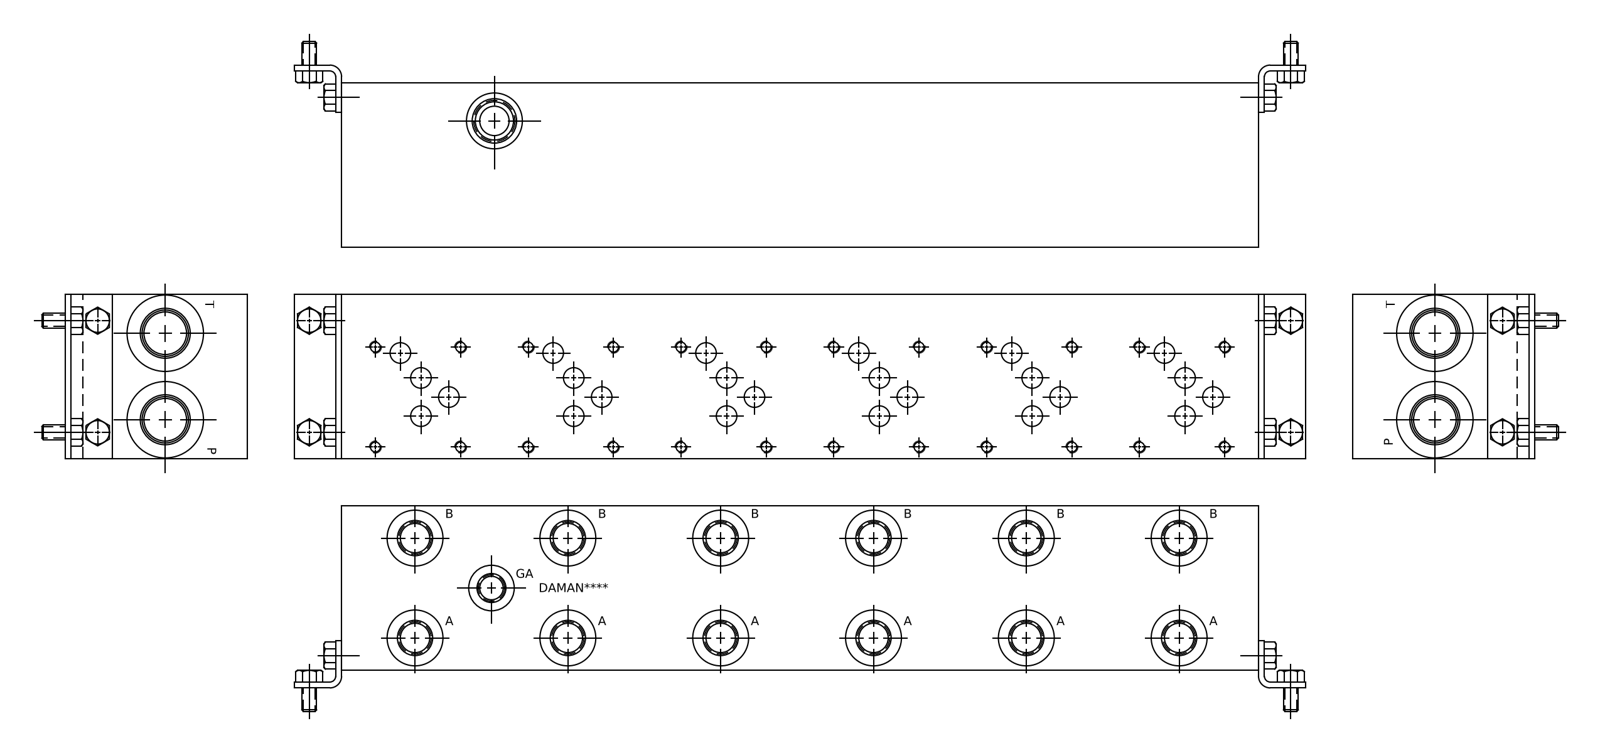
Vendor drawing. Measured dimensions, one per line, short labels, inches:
name: Part_AD05P063S_C_3D
written by: Autodesk Inventor 2020 (AUTOMOTIVE_DESIGN)
unit: in
bodies: 1 solid, 1038 faces (497 planar, 171 cylindrical, 370 other)
size: 19.5 × 3.5 × 3.5
volume: 226.7 in³; area: 367 in²
holes: 24× ⌀0.201, 24× ⌀0.25, 24× ⌀0.438, 12× ⌀0.625, 12× ⌀0.689, 12× ⌀0.75, 12× ⌀0.758, 12× ⌀1.206, 2× ⌀0.257, 2× ⌀0.312, 2× ⌀0.906, 2× ⌀0.981
face distances: 3.5, 0.031, 3.469, 19.5, 19.469, 19.438, 0.75, 0.562, 0.593, 2.907
hole spacings: 3.25, 6.5, 9.75, 3.883, 9.979, 6.839, 1.813, 2.125
